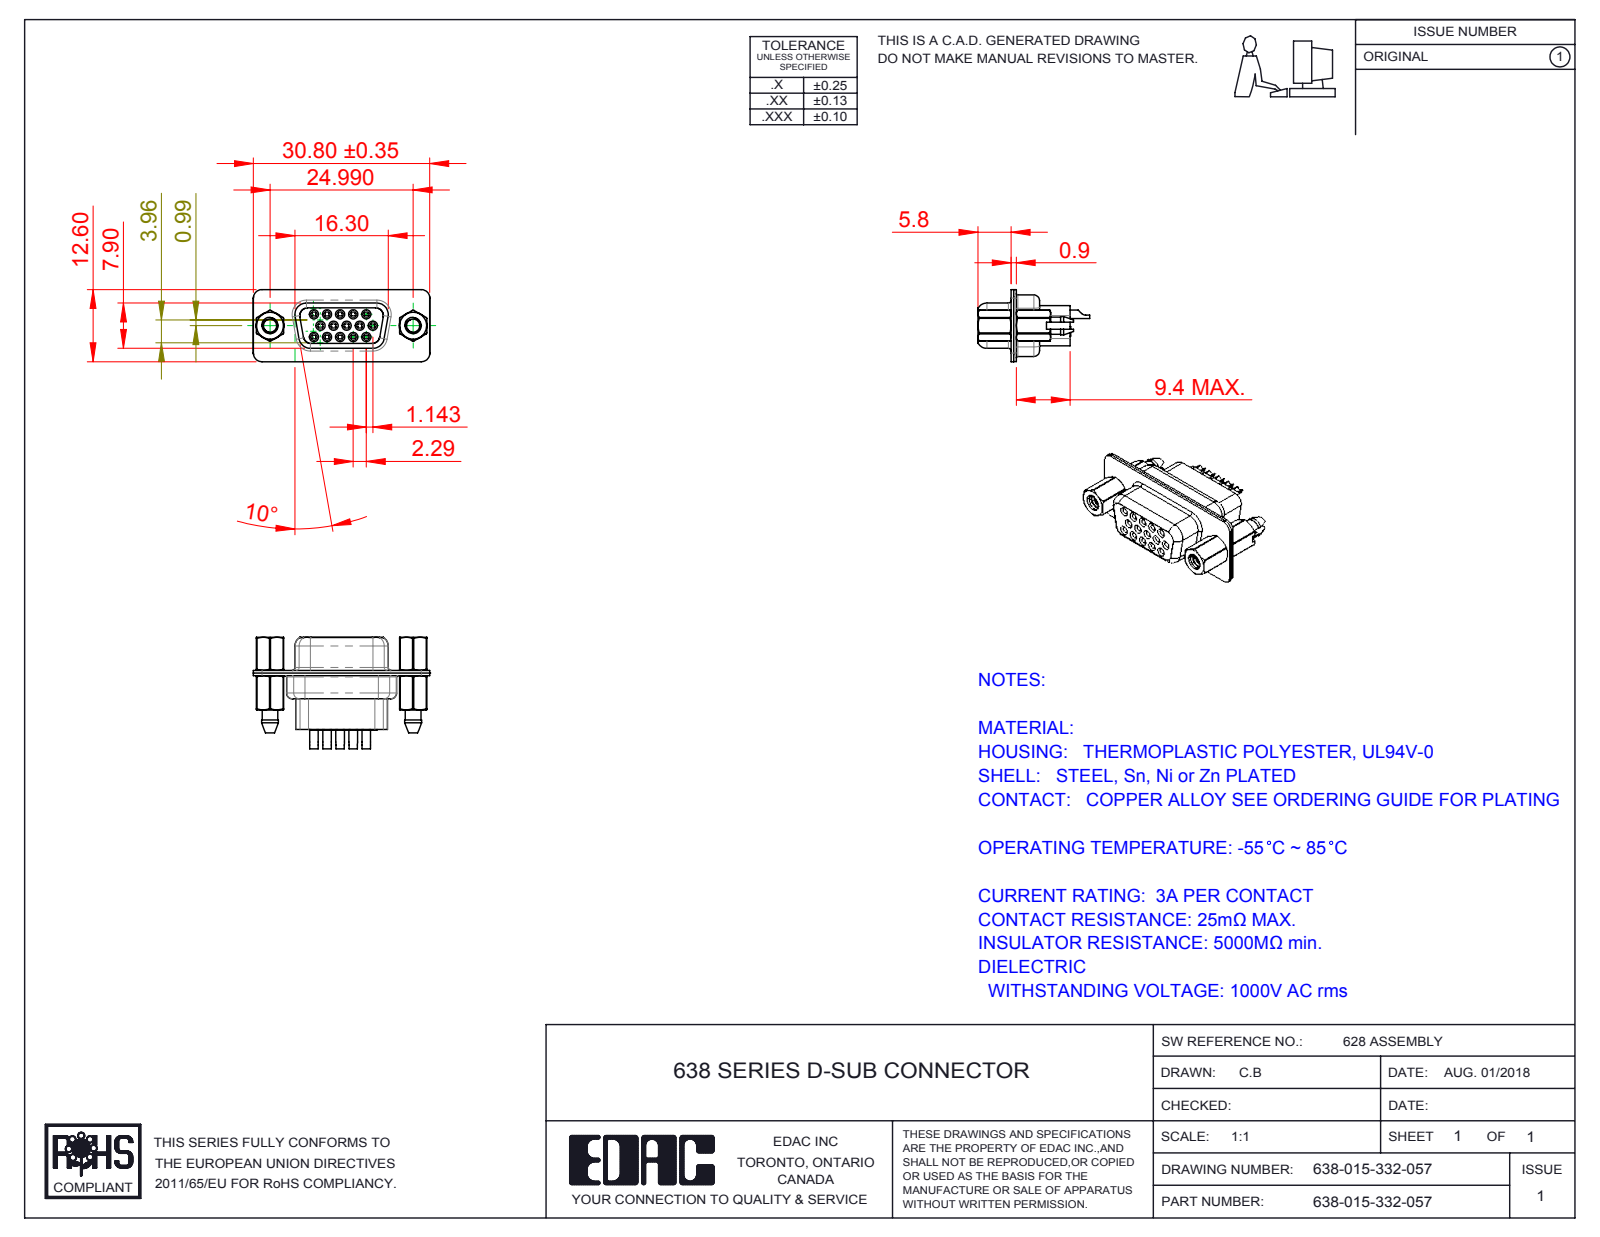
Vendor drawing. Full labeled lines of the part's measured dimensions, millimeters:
Part name (STEP PRODUCT): 638-015-332-057; 638 Housing_15 Contacts HP; 638 Shell Rear_15 Contacts; 638 Contact Row 3_32H (+5 more)
STEP written by: SolidWorks 2016 (CONFIG_CONTROL_DESIGN)
Units: millimetres
Bodies: 22 solids, 1814 faces (436 planar, 616 cylindrical, 762 other)
Overall size (bounding box): 30.81 × 19.5 × 12.6
Volume: 2 190 mm³ · Surface area: 7 083 mm²
Round holes (diameter × count): ⌀0.8 ×15, ⌀1 ×15, ⌀1.1 ×15, ⌀1.6 ×15, ⌀1.7 ×15, ⌀1.8 ×15, ⌀2 ×2, ⌀2.26 ×2, ⌀2.29 ×2, ⌀4 ×2, ⌀4.05 ×2, ⌀4.85 ×2
Round bosses / shafts (diameter × count): ⌀2 ×15, ⌀1.5 ×15, ⌀1.2 ×15, ⌀4.95 ×2, ⌀4.8 ×2, ⌀2.79 ×2
Partial cylindrical surfaces — rounded edges, fillets, slot ends (radius × count): R1.5 ×22, R2 ×12, R0.28 ×10, R1.55 ×8, R1 ×7, R1.35 ×5, R0.25 ×4, R0.5 ×4
Main face-to-face distances: 0.45, 0.9, 0.4, 1.43, 6.6, 8.88, 4.76, 7, 5.8, 2.28
Hole centre spacings: 3.96, 2.28, 4.57, 2.29, 6.05, 6.04, 6.86, 7.92
